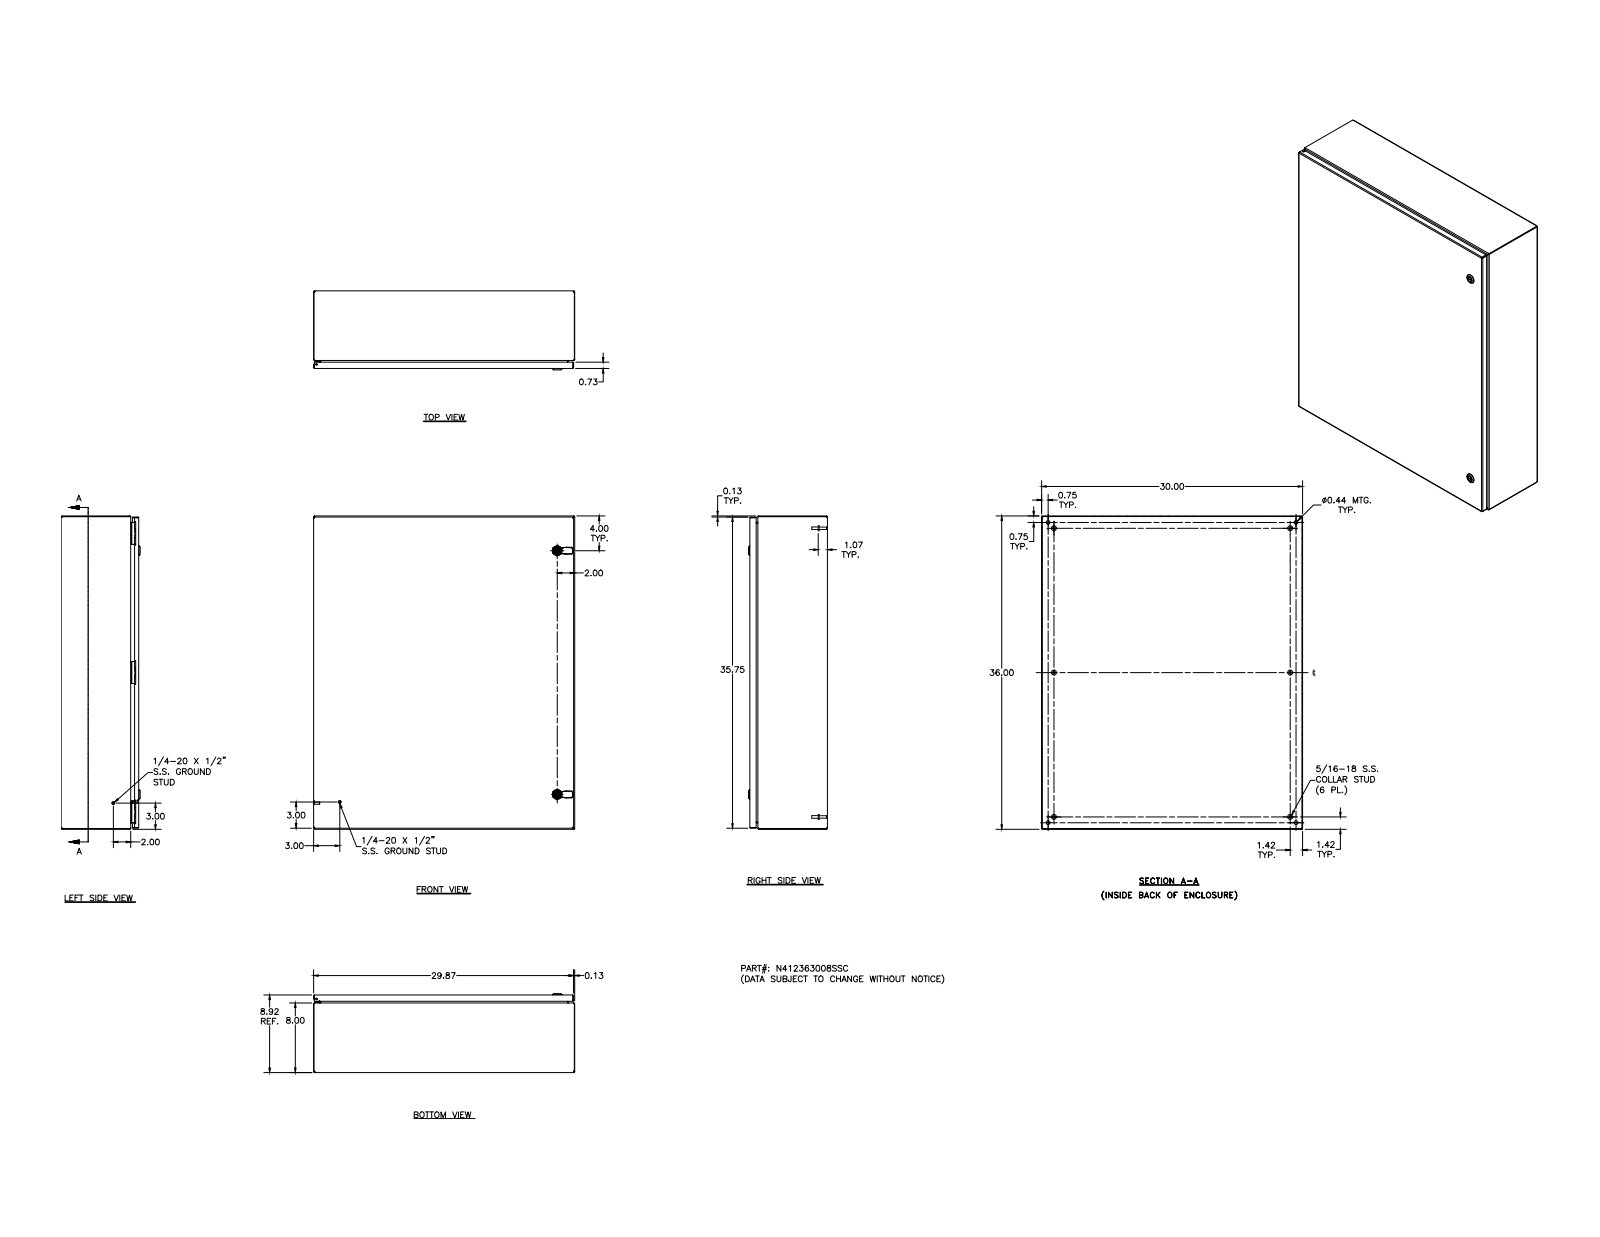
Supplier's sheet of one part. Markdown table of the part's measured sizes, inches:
| quantity | value |
| --- | --- |
| part name | N412363008SSC; N412363008SSCBKP; 388151; N4123630SSCLID (+8 more) |
| STEP written by | Autodesk Inventor 2011 (AUTOMOTIVE_DESIGN) |
| units | inches |
| bodies | 53 solids, 2118 faces (831 planar, 778 cylindrical, 509 other) |
| overall size | 36 × 30 × 9.075 |
| volume | 258.4 in³ |
| surface area | 7 010 in² |
| round holes (diameter × count) | 0.188 × 7, 0.093 × 6, 0.152 × 6, 0.167 × 6, 0.172 × 6, 0.437 × 4, 0.156 × 3, 0.197 × 2, 0.315 × 2, 0.394 × 2, 0.402 × 2, 0.634 × 2 |
| round bosses / shafts (diameter × count) | 0.25 × 14, 0.563 × 6, 0.36 × 6, 0.32 × 6, 0.3 × 6, 0.275 × 6, 0.256 × 6, 0.164 × 6 |
| partial cylindrical surfaces (radius × count) | 0.05 × 38, 0.031 × 34, 0.016 × 26, 0.125 × 21, 0.105 × 20, 0.02 × 15, 0.032 × 12, 0.07 × 8 |
| main face-to-face distances | 0.074, 8.843, 8.769, 8.917, 29.926, 35.926, 29.852, 30, 36, 35.852 |
| hole center spacings | 16.004, 32, 15.996, 0.017, 0.66, 15.992, 16, 16.008 |
